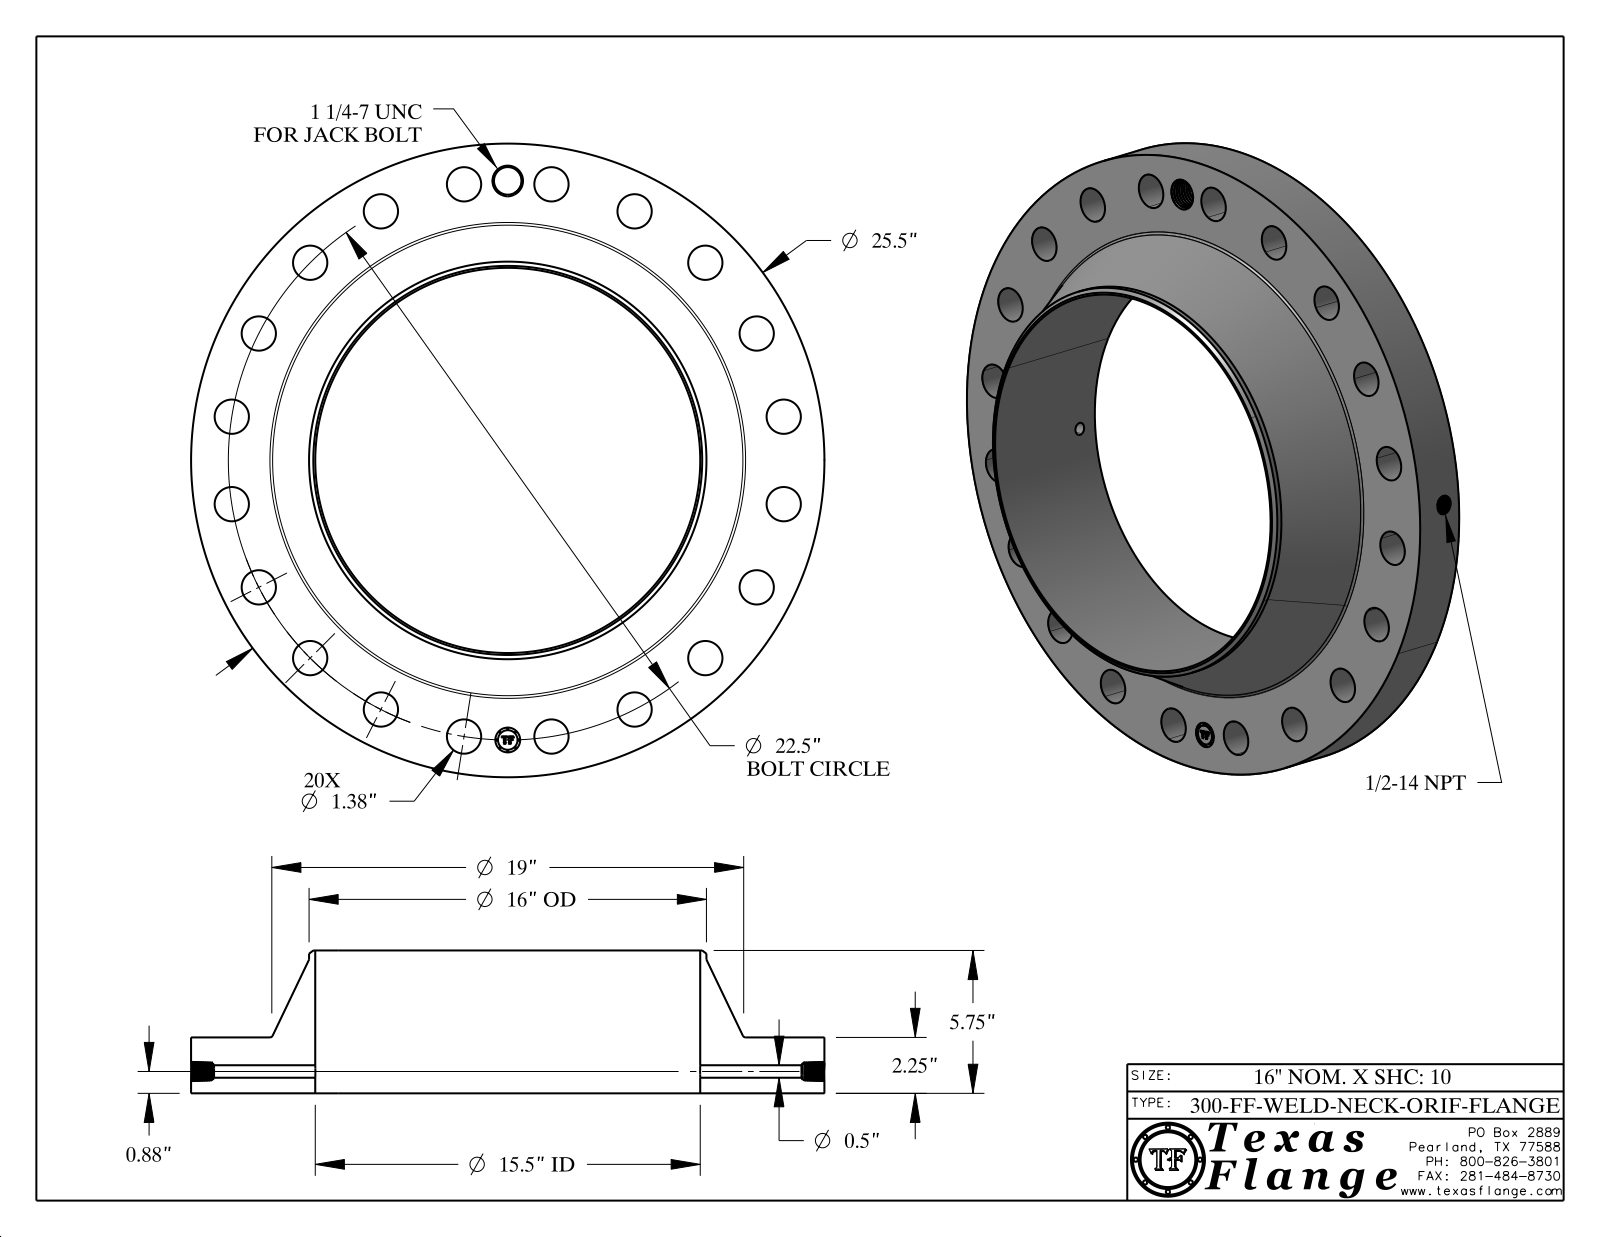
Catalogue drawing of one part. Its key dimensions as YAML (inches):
part_name: "300-FF-WELD-NECK"
step_written_by: "CATIA V5 STEP AP214 (AUTOMOTIVE_DESIGN)"
units: inches
bodies: {solids: 1, faces: 796, planar: 368, cylindrical: 117, other: 311}
overall_size: [25.5, 25.5, 5.75]
volume: 820.6
surface_area: 1390
round_holes:
  - {diameter: 1.38, count: 20}
  - {diameter: 0.5, count: 1}
  - {diameter: 0.672, count: 1}
  - {diameter: 1, count: 1}
  - {diameter: 1.109, count: 1}
  - {diameter: 15.5, count: 1}
round_bosses_or_shafts:
  - {diameter: 0.061, count: 8}
  - {diameter: 25.5, count: 1}
  - {diameter: 16, count: 1}
  - {diameter: 0.788, count: 1}
face_to_face_distances: [2.25, 5.75, 3.5, 2.235, 0.015, 3.515, 0.298, 0.293, 0.054, 0.248]
hole_center_spacings: [3.52, 10.215, 18.203, 20.048, 21.399, 6.953, 11.25, 13.225]
